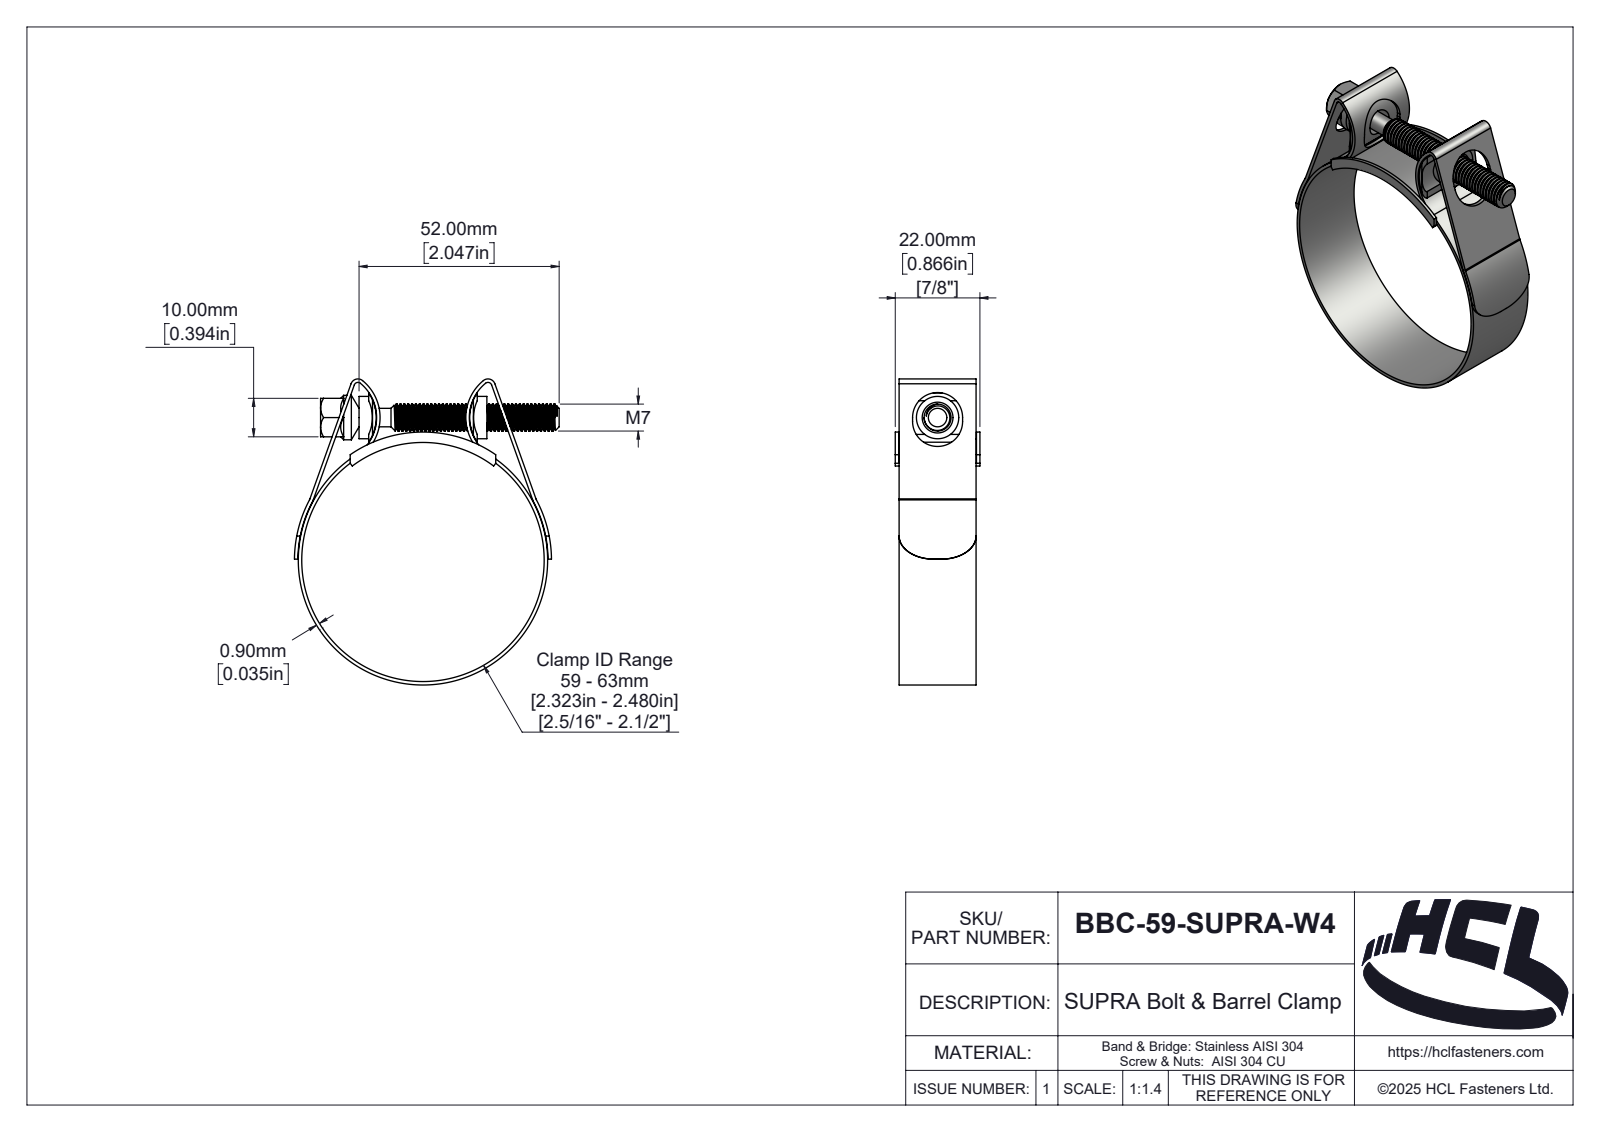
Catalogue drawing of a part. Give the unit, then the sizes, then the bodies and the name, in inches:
Units: inches
Overall size (bounding box): 3.13 × 2.708 × 0.866
Round holes (diameter × count): ⌀2.48 ×1
Round bosses / shafts (diameter × count): ⌀2.551 ×1, ⌀0.455 ×1, ⌀0.433 ×1, ⌀0.276 ×1, ⌀0.189 ×1
Partial cylindrical surfaces — rounded edges, fillets, slot ends (radius × count): R0.039 ×6, R0.075 ×2, R0.079 ×2, R0.114 ×2, R0.256 ×2, R0.41 ×2, R0.45 ×2, R0.454 ×2
Main face-to-face distances: 0.035, 0.787, 0.039, 0.827, 0.831, 0.791, 0.394, 0.866, 0.098, 1.209
Volume: 0.553 in³ · Surface area: 26.94 in²
Bodies: 5 solids, 321 faces (46 planar, 195 cylindrical, 80 other)
Part name (STEP PRODUCT): BBC-59-SUPRA-W4
STEP written by: SolidWorks 2025 (AUTOMOTIVE_DESIGN)
